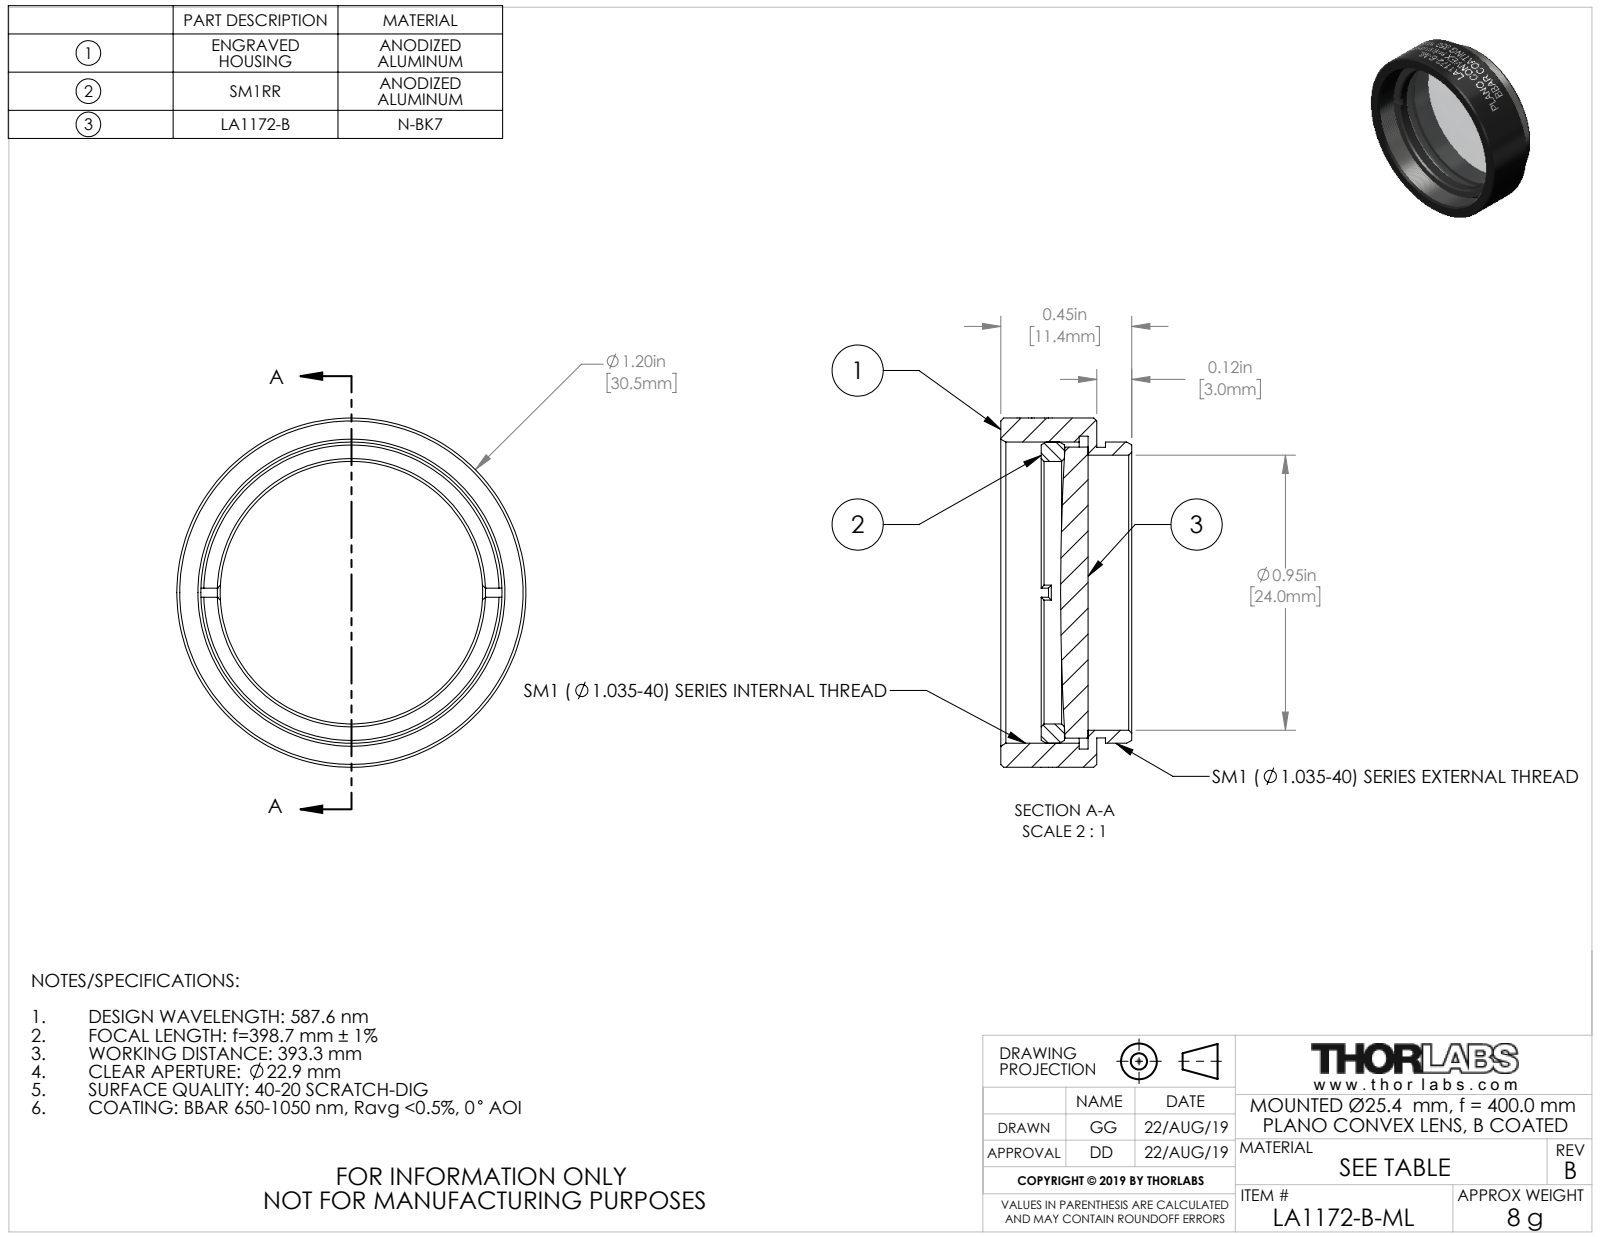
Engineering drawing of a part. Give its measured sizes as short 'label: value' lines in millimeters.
name: 24448-E0W
written by: SolidWorks 2018 (CONFIG_CONTROL_DESIGN)
unit: mm
bodies: 3 solids, 155 faces (20 planar, 111 cylindrical, 24 other)
size: 30.48 × 30.48 × 11.43
volume: 3 193 mm³; area: 4 313 mm²
holes: 1× ⌀22.91, 1× ⌀24, 1× ⌀26.29, 1× ⌀27.3
bosses: 1× ⌀30.48, 1× ⌀26.29, 1× ⌀25.4, 1× ⌀25.37
face distances: 0.76, 8.38, 7.62, 2.82, 2.06, 5.56, 4.85, 4.09, 2.03, 3.53
